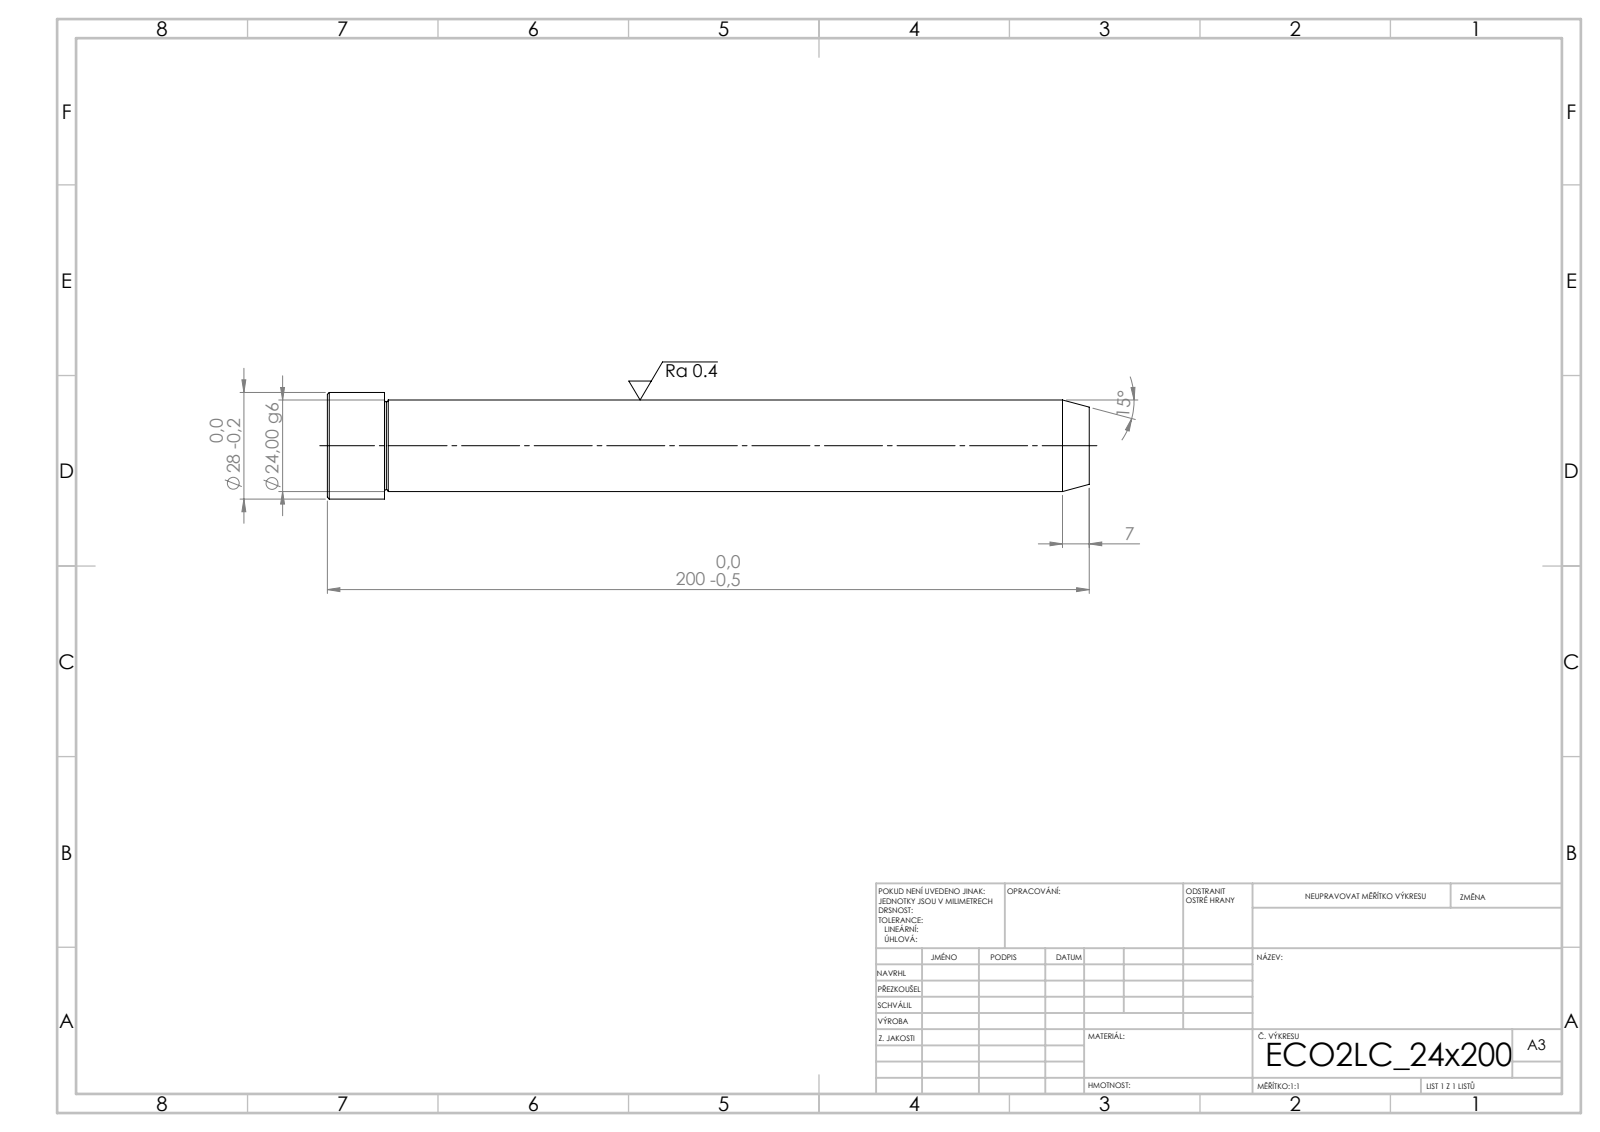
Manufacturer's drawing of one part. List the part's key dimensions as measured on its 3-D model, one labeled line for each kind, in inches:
STEP written by: SolidWorks 2019 (CONFIG_CONTROL_DESIGN)
Units: inches
Bodies: 1 solid, 15 faces (3 planar, 4 cylindrical, 8 other)
Overall size (bounding box): 7.874 × 1.102 × 1.102
Volume: 5.64 in³ · Surface area: 25.36 in²
Round bosses / shafts (diameter × count): ⌀1.102 ×1, ⌀0.945 ×1
Main face-to-face distances: 7.874, 7.283, 0.591
